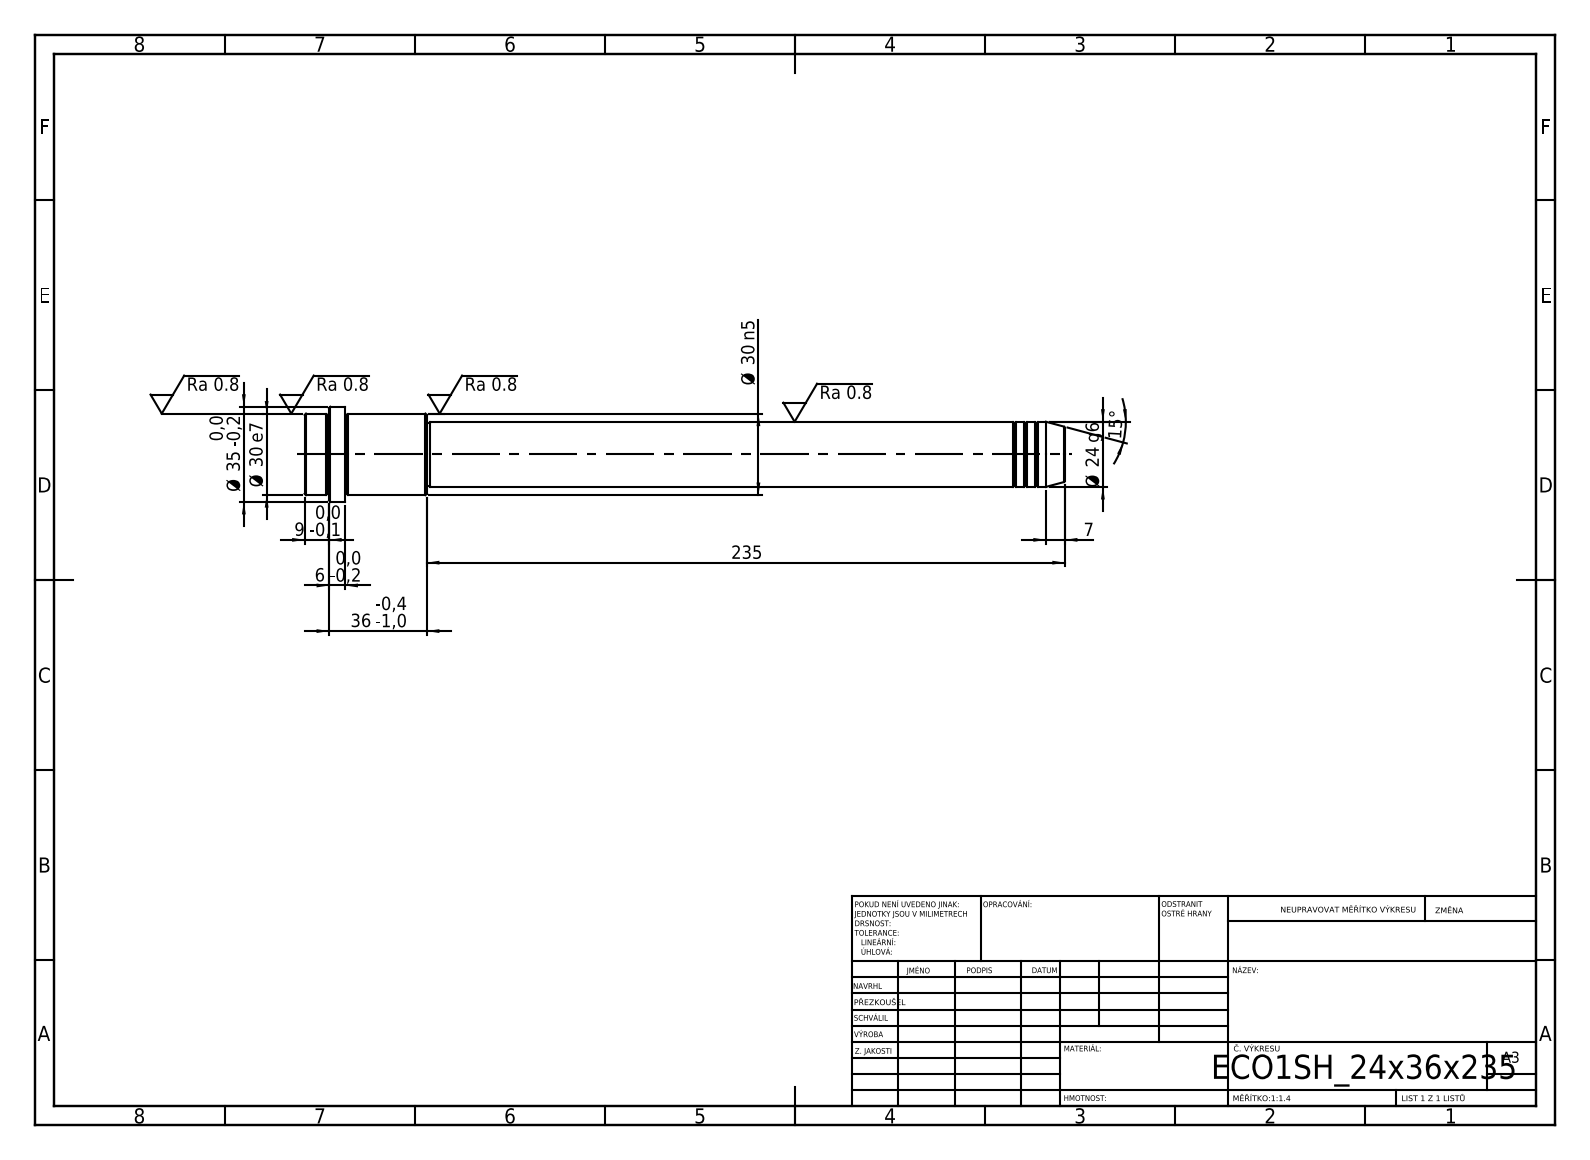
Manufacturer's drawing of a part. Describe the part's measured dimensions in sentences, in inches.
Its 3-D file was written by "SolidWorks 2019 (CONFIG_CONTROL_DESIGN)". It is 1 solid with 52 faces: 6 planar, 16 cylindrical and 30 other. Overall it measures 11.024 by 1.378 by 1.378 inches. Its volume is 8.479 cubic inches and its surface area 37.23 square inches. Round bosses or shafts: 1 of diameter 1.378, 1 of diameter 1.181, 1 of diameter 0.945, 1 of diameter 0.906. The main face-to-face distances are 11.024, 10.433, 0.591, 9.252, 1.181, 1.772, 10.669, 1.417, 0.236, 0.354.
